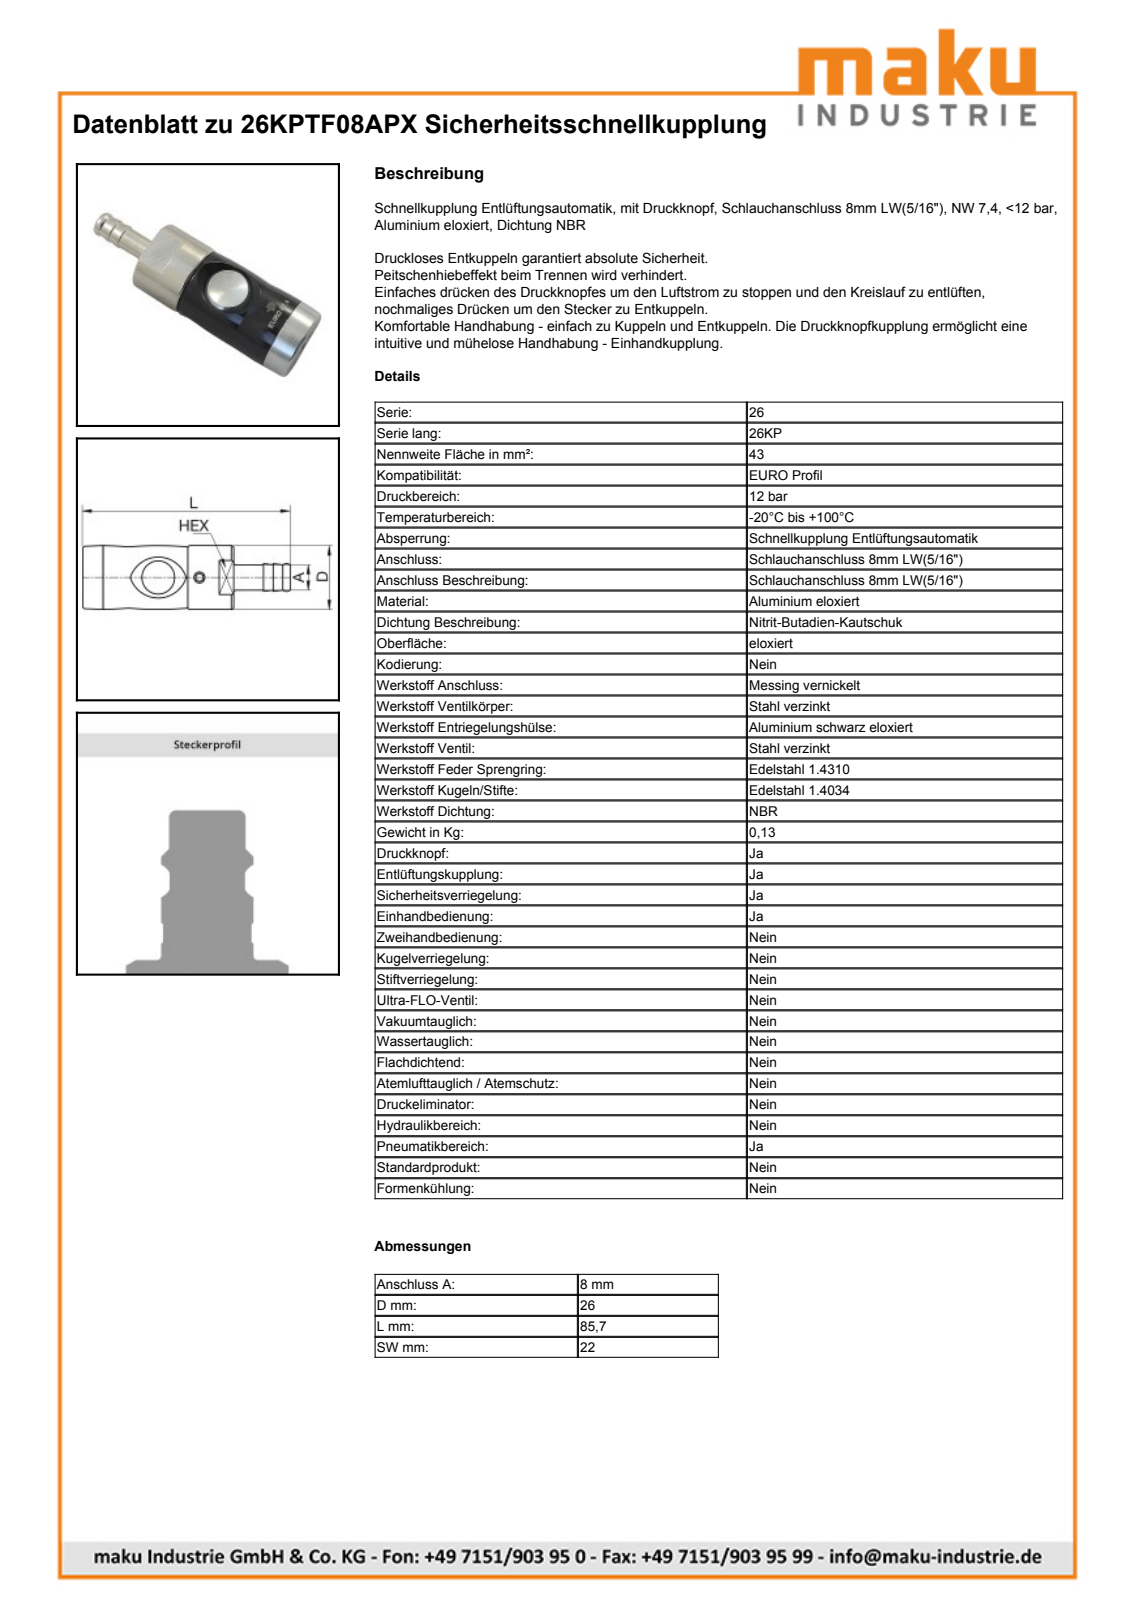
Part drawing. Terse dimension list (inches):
name: 26KPTF08APX
written by: Autodesk Inventor 2019 (AUTOMOTIVE_DESIGN)
unit: in
bodies: 37 solids, 211 faces (60 planar, 66 cylindrical, 85 other)
size: 3.374 × 1.024 × 1.024
volume: 2.321 in³; area: 37.7 in²
holes: 2× ⌀0.488, 1× ⌀0.138, 1× ⌀0.236, 1× ⌀0.256, 1× ⌀0.378, 1× ⌀0.38, 1× ⌀0.417, 1× ⌀0.474, 1× ⌀0.482, 1× ⌀0.535, 1× ⌀0.591, 1× ⌀0.654
bosses: 1× ⌀1.024, 1× ⌀0.884, 1× ⌀0.866, 1× ⌀0.807, 1× ⌀0.713, 1× ⌀0.65, 1× ⌀0.629, 1× ⌀0.622
rounds: 2× R0.244
face distances: 0.748, 0.331, 1.709, 2.457, 2.126, 1.378, 0.051, 2.406, 1.657, 0.28
hole spacings: 0.024, 0.028, 0.051, 0.671
